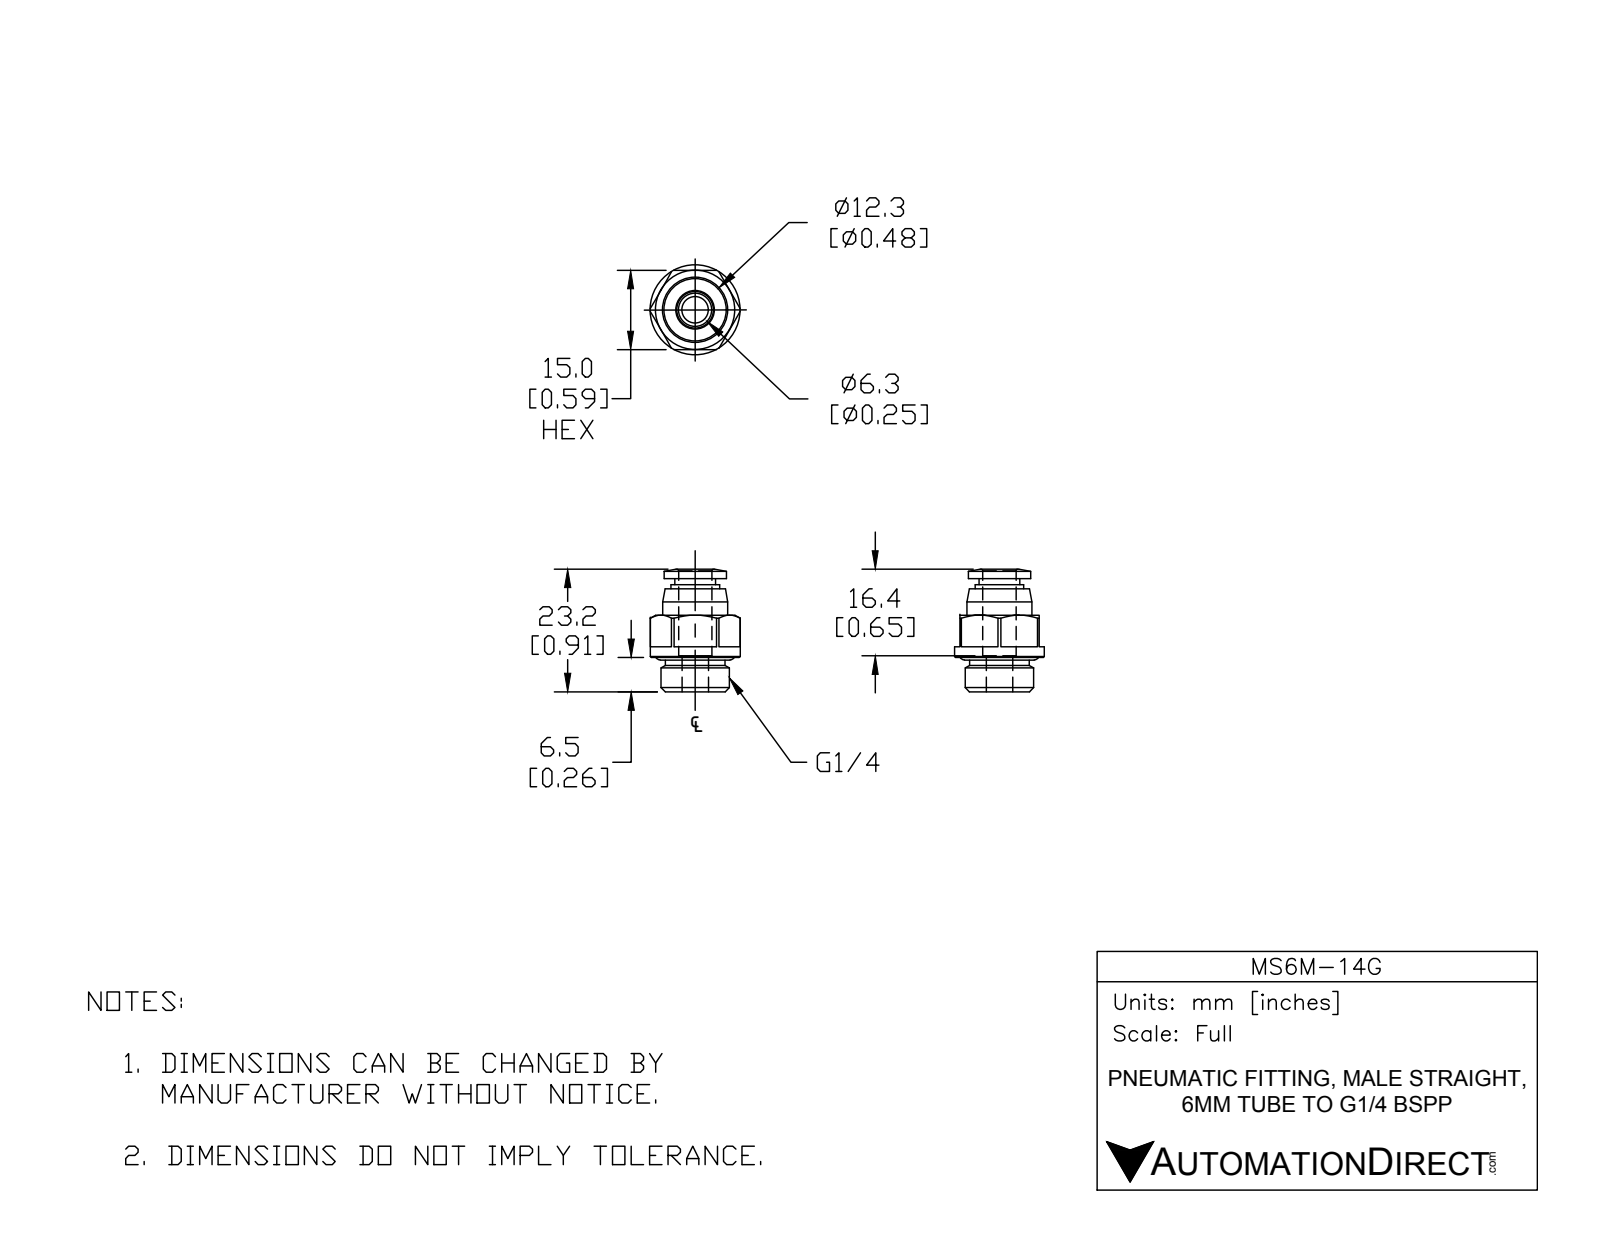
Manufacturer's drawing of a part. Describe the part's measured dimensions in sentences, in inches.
The part is named "MS6M-14G". Its 3-D file was written by "SolidWorks 2018 (AUTOMOTIVE_DESIGN)". It is 1 solid with 61 faces: 21 planar, 18 cylindrical and 22 other. Overall it measures 0.913 by 0.669 by 0.669 inches. Its volume is 0.161 cubic inches and its surface area 3.318 square inches. Round holes: 1 of diameter 0.197, 1 of diameter 0.248. Round bosses or shafts: 1 of diameter 0.669, 1 of diameter 0.51, 1 of diameter 0.484, 1 of diameter 0.465, 1 of diameter 0.445, 1 of diameter 0.362, 1 of diameter 0.303. The main face-to-face distances are 0.591, 0.843, 0.571, 0.272, 0.768, 0.197, 0.075, 0.335, 0.236, 0.433.
